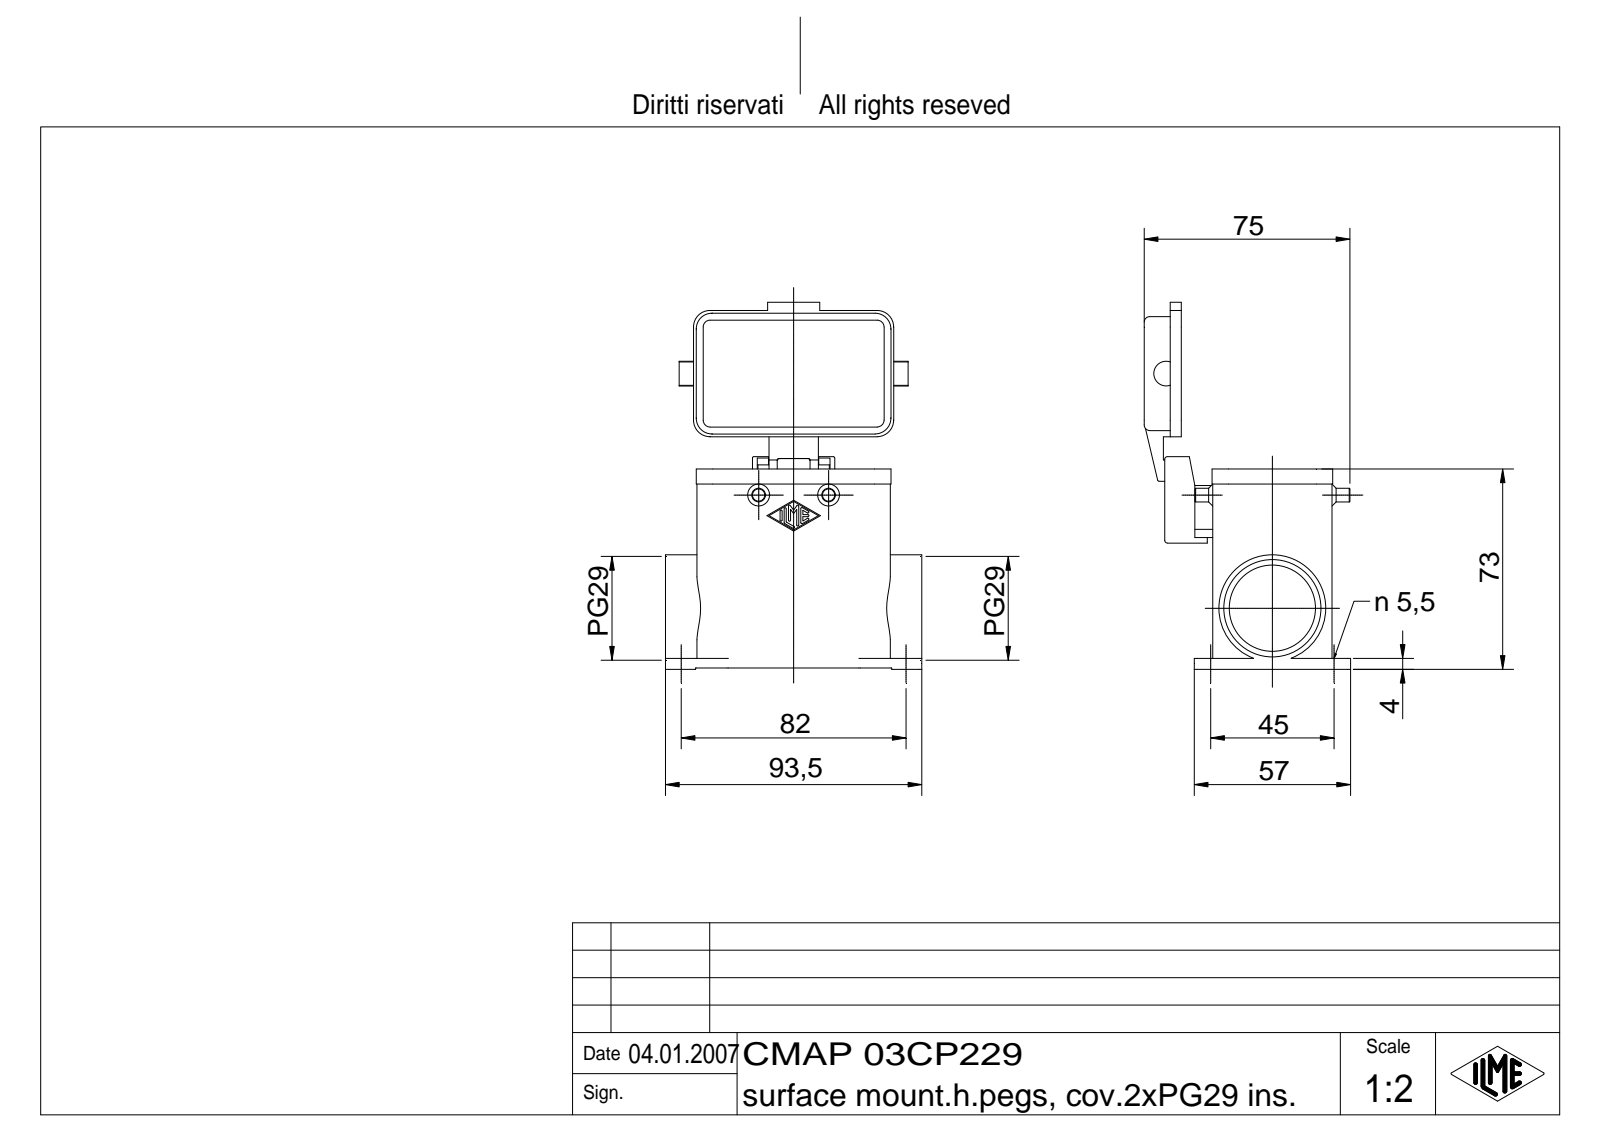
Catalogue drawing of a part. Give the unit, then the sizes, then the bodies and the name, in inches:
Units: inches
Overall size (bounding box): 5.266 × 3.681 × 2.963
Round holes (diameter × count): ⌀0.217 ×4, ⌀0.157 ×1, ⌀0.197 ×1, ⌀1.239 ×1, ⌀1.397 ×1
Round bosses / shafts (diameter × count): ⌀0.197 ×2, ⌀0.118 ×2, ⌀1.535 ×1, ⌀0.276 ×1, ⌀0.157 ×1
Partial cylindrical surfaces — rounded edges, fillets, slot ends (radius × count): R0.015 ×14, R0.039 ×14, R0.236 ×12, R0.02 ×10, R0.028 ×8, R0.079 ×8, R0.098 ×4, R0.118 ×4
Main face-to-face distances: 0.118, 1.594, 1.713, 0.098, 2.697, 1.476, 2.598, 0.886, 0.138, 2.48
Hole centre spacings: 1.772, 3.228, 3.683
Volume: 5.893 in³ · Surface area: 94.66 in²
Bodies: 1 solid, 473 faces (197 planar, 166 cylindrical, 110 other)
Part name (STEP PRODUCT): CMAP 03CP229
STEP written by: Autodesk Inventor 7 (AUTOMOTIVE_DESIGN)
